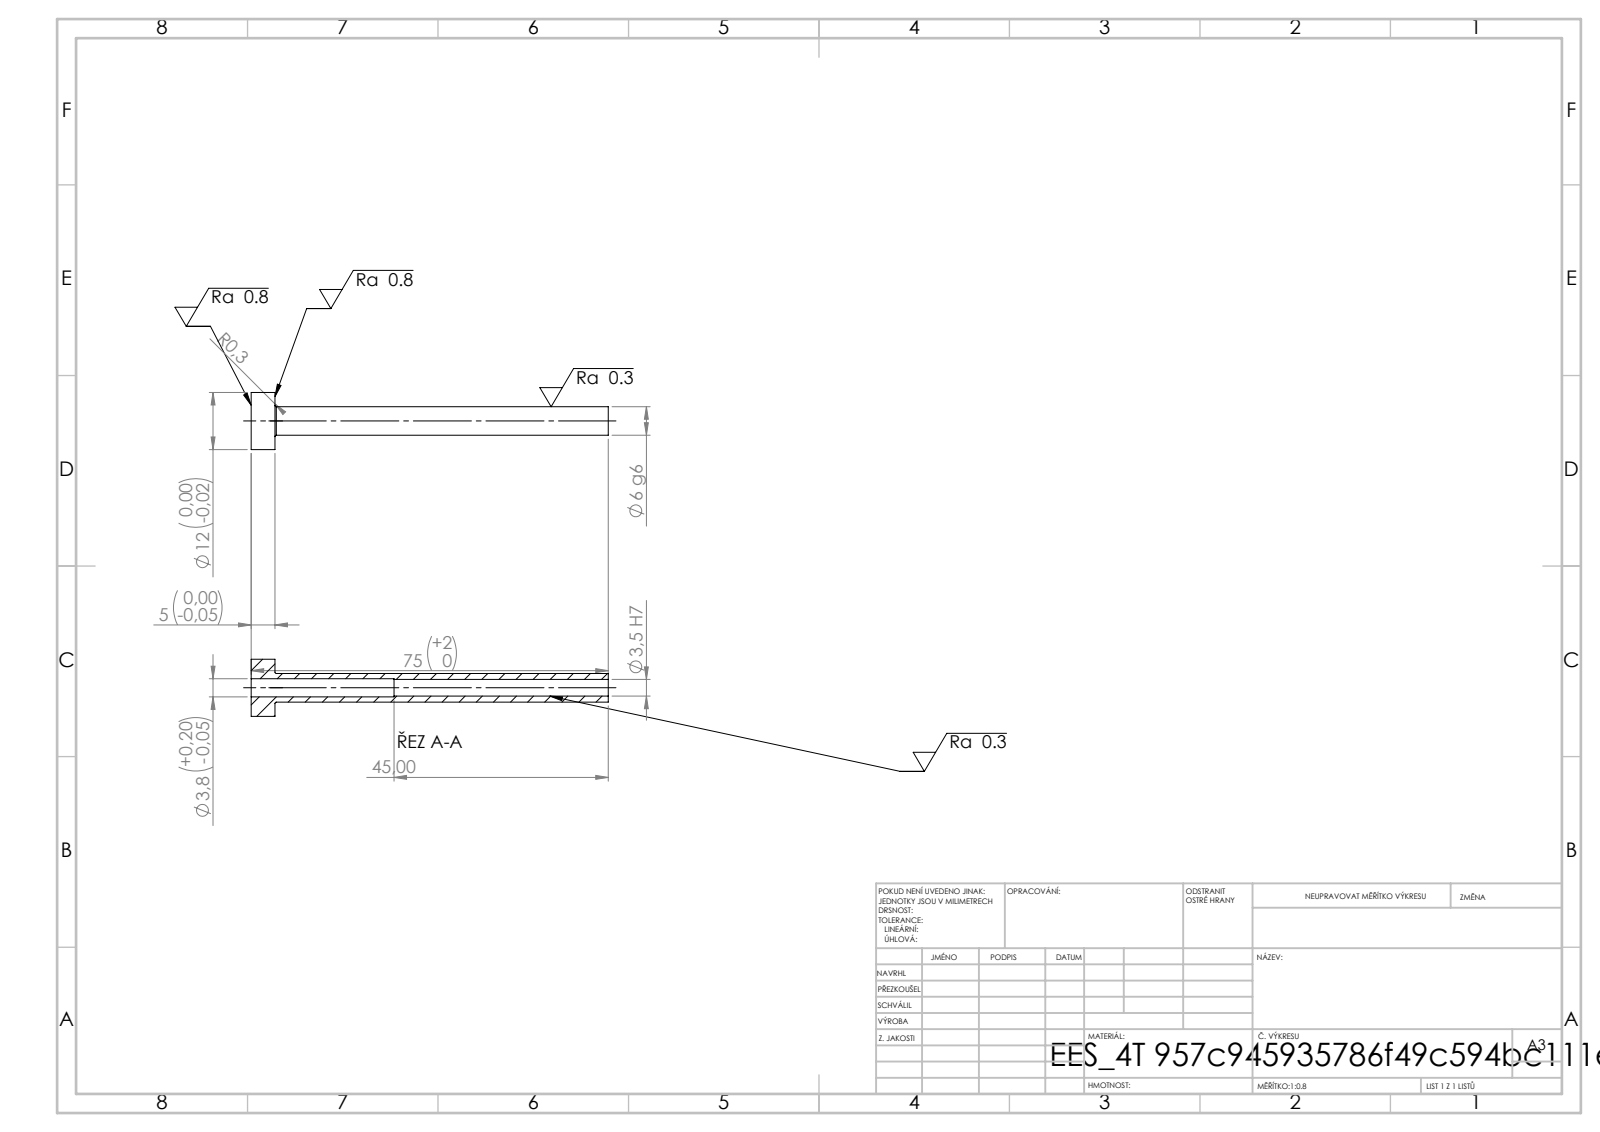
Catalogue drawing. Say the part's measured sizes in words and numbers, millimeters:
Its 3-D file was written by "SolidWorks 2019 (CONFIG_CONTROL_DESIGN)". It is 1 solid with 14 faces: 4 planar, 8 cylindrical and 2 other. Overall it measures 75 by 12 by 12 millimeters. Its volume is 1 772 cubic millimeters and its surface area 2 565 square millimeters. Round holes: 1 of diameter 3.5, 1 of diameter 3.8. Round bosses or shafts: 1 of diameter 12, 1 of diameter 6. The main face-to-face distances are 5, 75, 70, 30, 25, 45.
